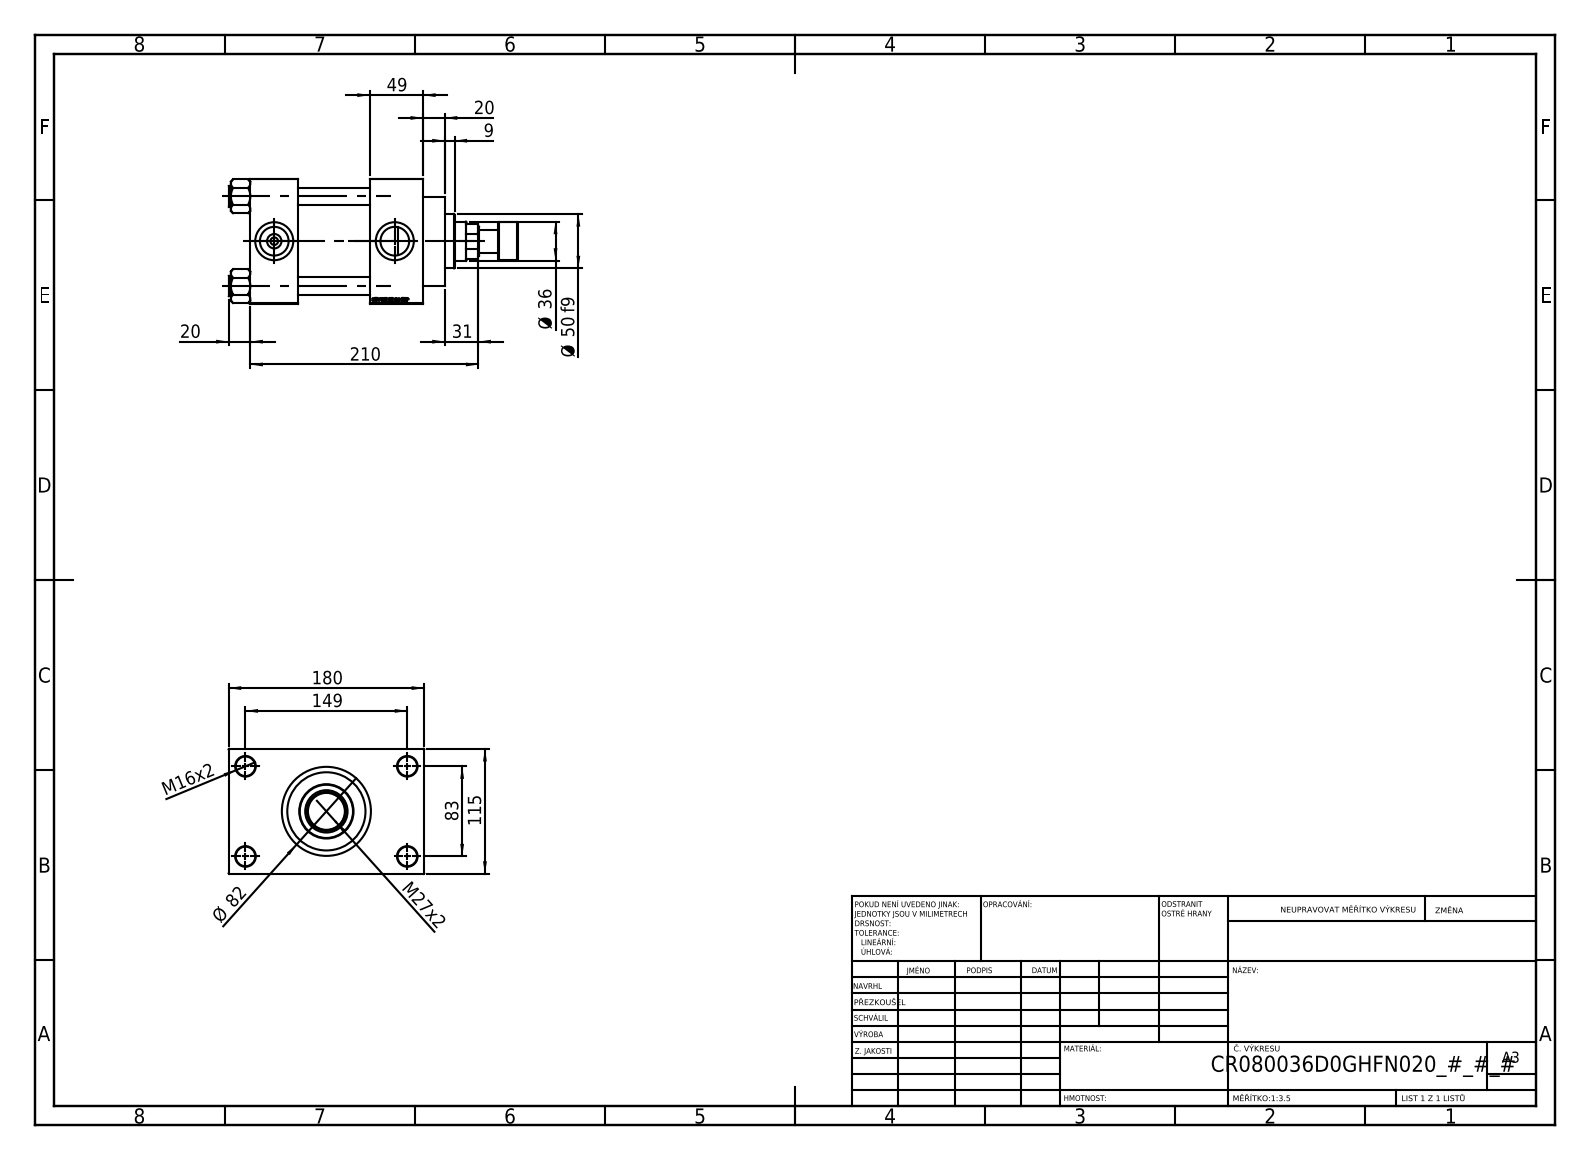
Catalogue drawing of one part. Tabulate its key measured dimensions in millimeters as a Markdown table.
| quantity | value |
| --- | --- |
| part name | NUT_M5_D; V215CR_ROD_END_F; V215CR_D_Body; V215CR_D_TYCINKA (+2 more) |
| STEP written by | SolidWorks 2019 (CONFIG_CONTROL_DESIGN) |
| units | millimeters |
| bodies | 12 solids, 1165 faces (549 planar, 92 cylindrical, 524 other) |
| overall size | 266 × 180 × 115 |
| volume | 2 003 000 mm³ |
| surface area | 302 161 mm² |
| round holes (diameter × count) | 16 × 4, 18 × 4, 7 × 2, 26.44 × 2, 35 × 2, 25.5 × 1, 36 × 1, 39 × 1, 61 × 1, 72 × 1, 80 × 1 |
| round bosses / shafts (diameter × count) | 19 × 4, 86 × 1, 82 × 1, 50 × 1, 35 × 1, 21 × 1 |
| main face-to-face distances | 115, 66, 49, 110, 44, 159, 32.5, 147.5, 20, 69 |
| hole center spacings | 33.15, 58.48, 82.7, 85.28, 89.24, 115.85, 142.43, 83 |
